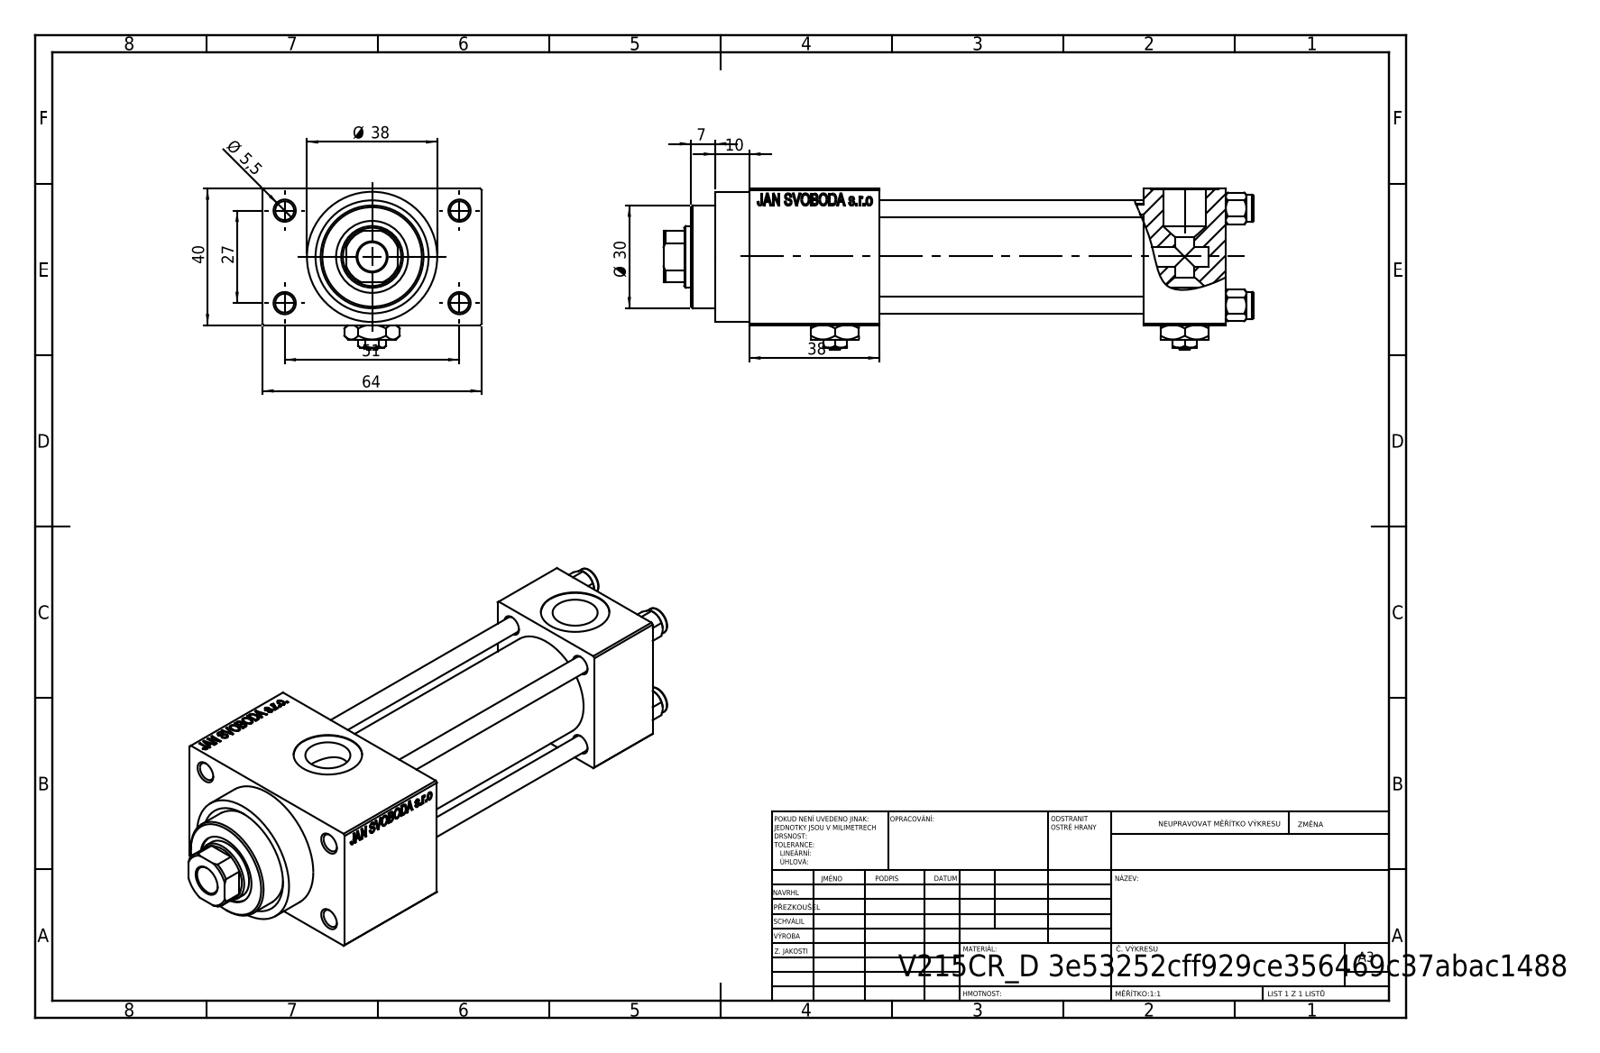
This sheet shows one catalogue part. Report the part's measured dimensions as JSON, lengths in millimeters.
{"part_name": "V215CR_VCP_D; V215CR_D_Body; Zatka_pro_OIL_PORT; NUT_M5_D (+2 more)", "step_written_by": "SolidWorks 2019 (CONFIG_CONTROL_DESIGN)", "units": "millimeters", "bodies": {"solids": 13, "faces": 1201, "planar": 541, "cylindrical": 98, "other": 562}, "overall_size": [172, 64, 47], "volume_mm3": 197560, "surface_area_mm2": 74644, "round_holes": [[5, 4], [5.5, 4], [20, 3], [7, 2], [13.16, 2], [8.5, 1], [18, 1], [21, 1], [25, 1], [30, 1]], "round_bosses_or_shafts": [[8, 4], [38, 1], [31, 1]], "partial_cylinders_radius": [[8.5, 1]], "face_to_face_distances": [40, 12, 52, 77, 24, 101, 64, 38, 115, 139], "hole_center_spacings": [11.37, 20.01, 28.3, 28.85, 29.89, 39.66, 48.34, 27]}
